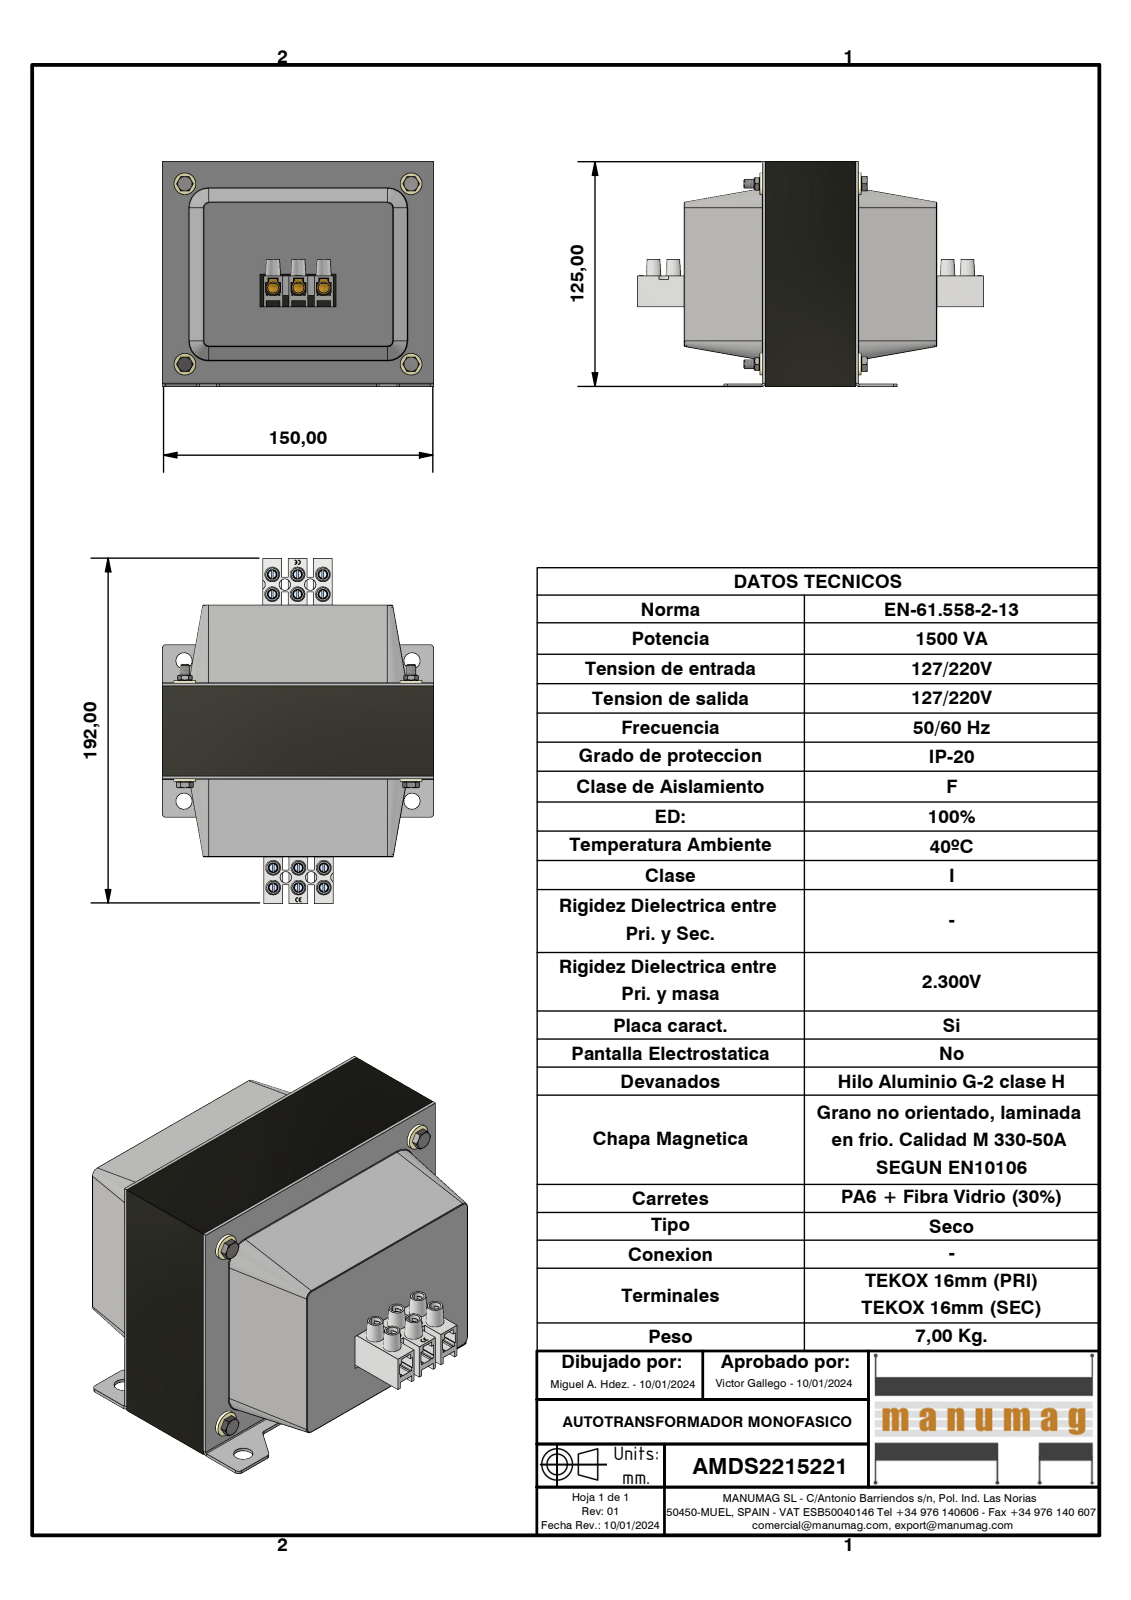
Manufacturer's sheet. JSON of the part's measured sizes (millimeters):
{"part_name": "AMDS2215221; centrador M5; DIN 934 - M4 x 0,7; EI150 x 125 - 50 (RC50) Negro (+8 more)", "step_written_by": "Autodesk Inventor 2023 (AUTOMOTIVE_DESIGN)", "units": "millimeters", "bodies": {"solids": 51, "faces": 2186, "planar": 1484, "cylindrical": 282, "other": 420}, "overall_size": [192, 150, 125], "volume_mm3": 825027, "surface_area_mm2": 259228, "round_holes": [[3.24, 16], [5.5, 12], [6, 10], [5, 4], [6.3, 4], [8, 4], [9, 4]], "round_bosses_or_shafts": [[4, 12], [12, 4], [6.7, 4], [5.9, 4], [4.57, 4]], "partial_cylinders_radius": [[2.75, 18], [0.38, 16], [0.82, 16], [2, 14], [3, 12], [0.81, 8], [0.1, 6], [0.22, 6]], "face_to_face_distances": [1.5, 50, 95, 43.5, 25, 102.9, 100, 45, 93.5, 42], "hole_center_spacings": [14, 9, 17.8, 11, 28, 163, 8.8, 8.81]}
